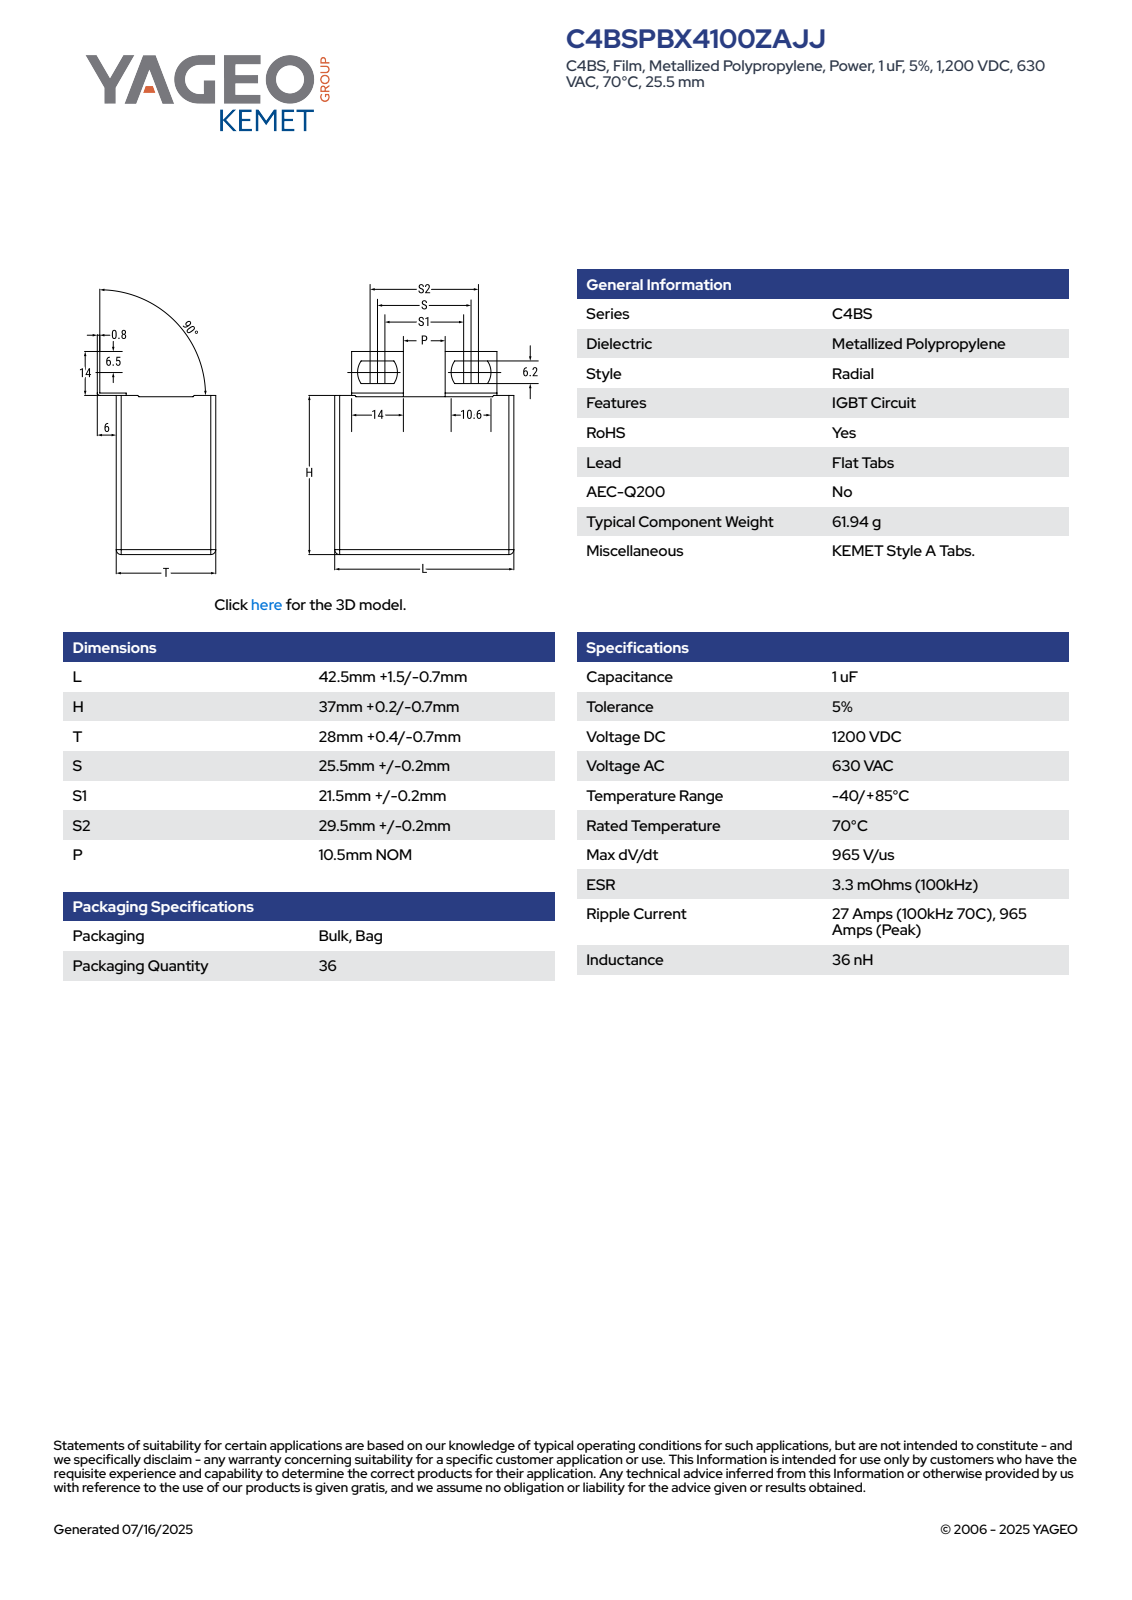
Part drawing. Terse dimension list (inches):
name: CFP_C4BA_42.5X37X28_L44H37.2T28.4S25.7
written by: SolidWorks 2014 (AUTOMOTIVE_DESIGN)
unit: in
bodies: 4 solids, 97 faces (91 planar, 6 cylindrical, 0 other)
size: 2.039 × 1.732 × 1.355
volume: 2.86 in³; area: 14.93 in²
rounds: 4× R0.24
face distances: 1.118, 1.463, 1.732, 0.024, 1.465, 1.488, 0.026, 1.354, 0.236, 1.331
